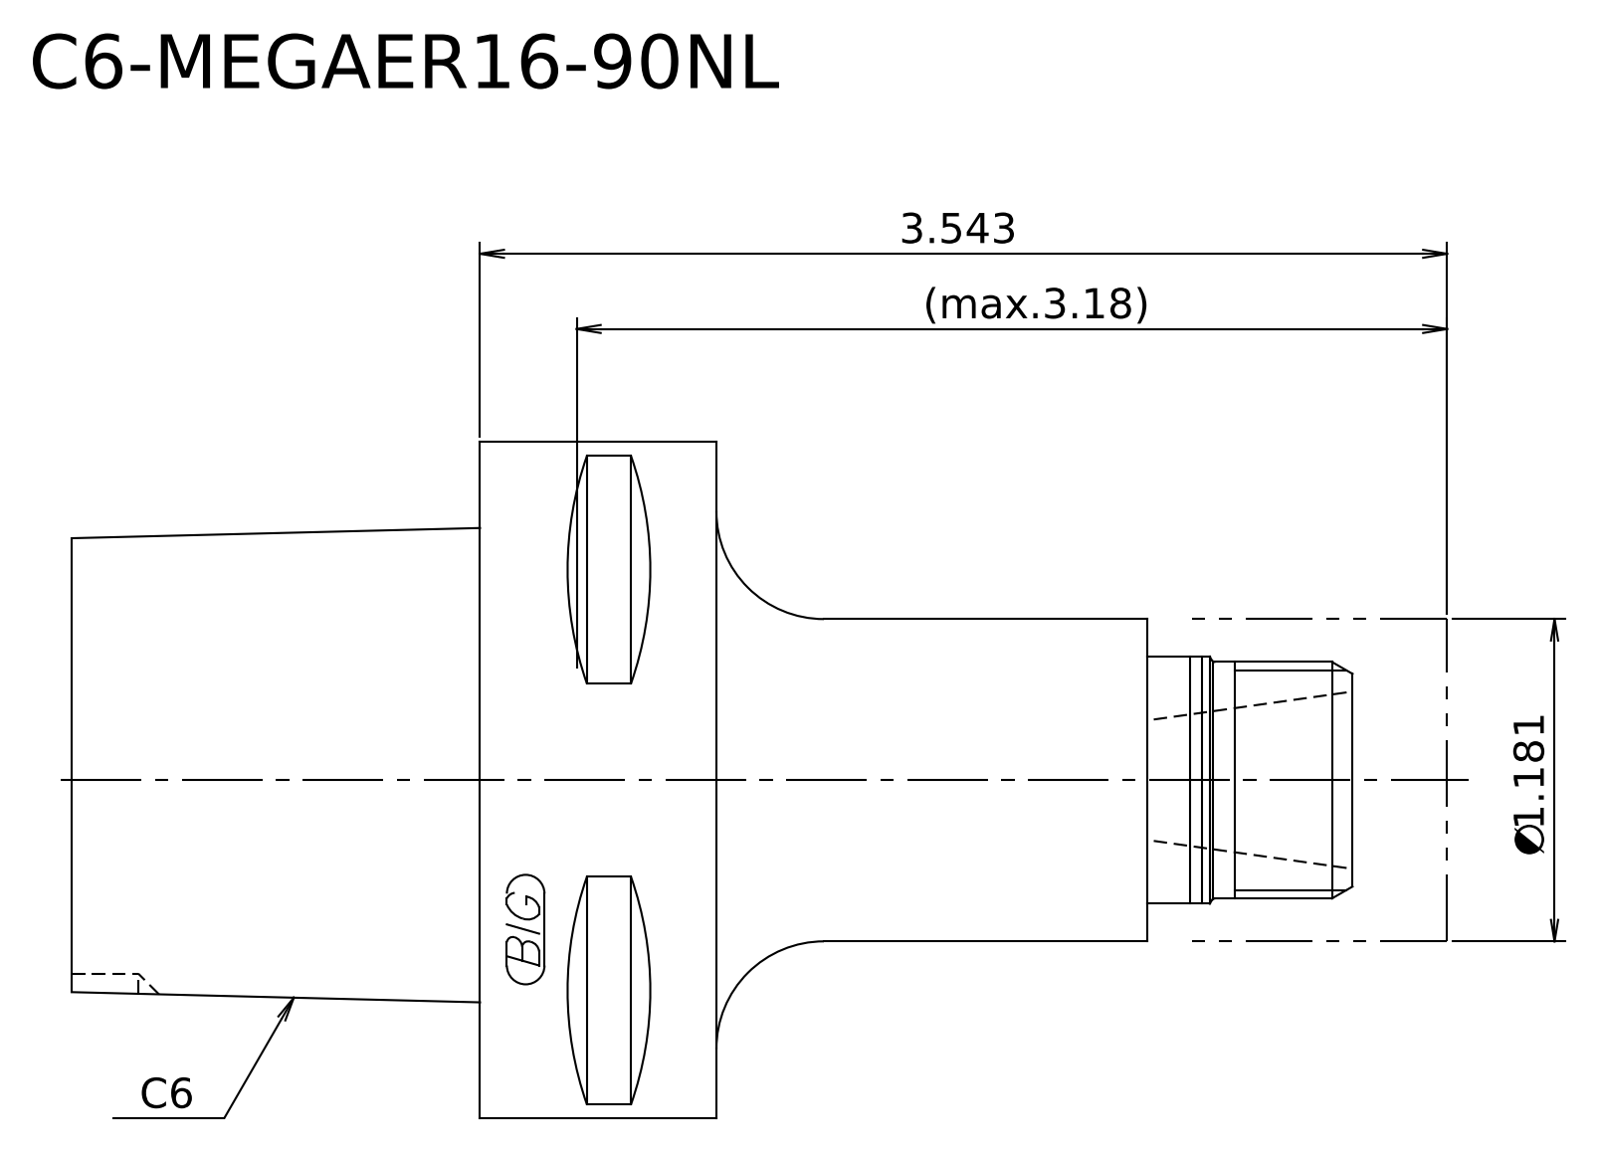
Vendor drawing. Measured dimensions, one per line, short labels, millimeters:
written by: Kubotek KeyCreator 2011 V10.0.2 (22737) (automotive_design)
unit: mm
bodies: 2 solids, 18 faces (7 planar, 5 cylindrical, 6 other)
size: 128 × 63 × 63
volume: 182 528 mm³; area: 24 010 mm²
bosses: 1× ⌀63, 1× ⌀30, 1× ⌀23, 1× ⌀22
face distances: 38, 22, 60, 43, 65, 103, 25, 68, 90, 128
